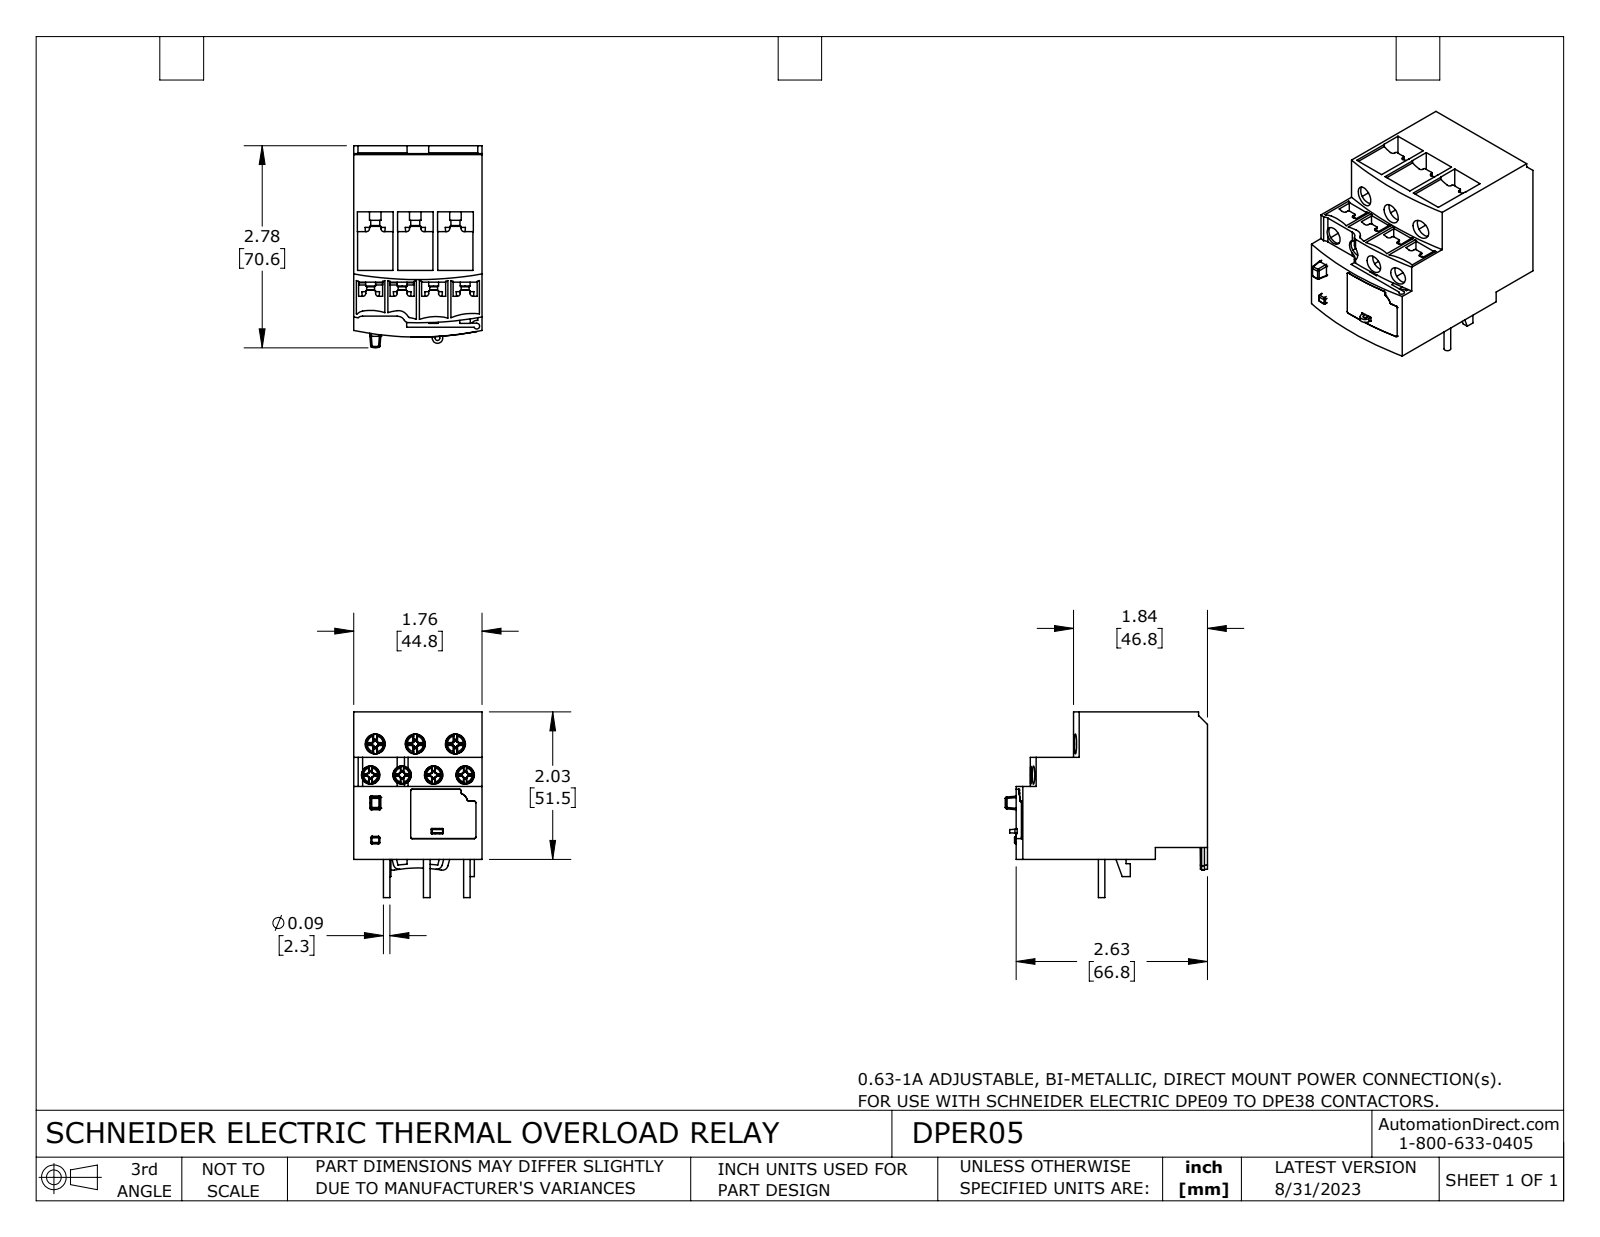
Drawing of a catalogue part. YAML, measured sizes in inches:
part_name: "DPER05"
step_written_by: "SolidWorks 2021 (CONFIG_CONTROL_DESIGN)"
units: inches
bodies: {solids: 16, faces: 1212, planar: 676, cylindrical: 269, other: 267}
overall_size: [2.778, 2.553, 1.764]
volume: 6.953
surface_area: 47.15
round_holes:
  - {diameter: 0.252, count: 4}
  - {diameter: 0.276, count: 3}
  - {diameter: 0.079, count: 2}
  - {diameter: 0.118, count: 2}
  - {diameter: 0.059, count: 1}
  - {diameter: 0.244, count: 1}
round_bosses_or_shafts:
  - {diameter: 0.091, count: 12}
  - {diameter: 0.138, count: 4}
  - {diameter: 0.108, count: 4}
  - {diameter: 0.157, count: 3}
  - {diameter: 0.154, count: 3}
  - {diameter: 0.124, count: 3}
  - {diameter: 0.118, count: 1}
  - {diameter: 0.107, count: 1}
partial_cylinders:
  - {radius: 0.02, count: 52}
  - {radius: 0.039, count: 22}
  - {radius: 0.004, count: 19}
  - {radius: 0.012, count: 8}
  - {radius: 0.008, count: 6}
  - {radius: 0.63, count: 6}
  - {radius: 0.079, count: 4}
  - {radius: 0.024, count: 2}
face_to_face_distances: [1.764, 0.165, 2.028, 1.863, 0.909, 0.551, 0.618, 1.409, 1.245, 2.497]
hole_center_spacings: [0.433, 0.551, 0.866, 0.334, 0.381, 0.404, 0.422, 0.449]
